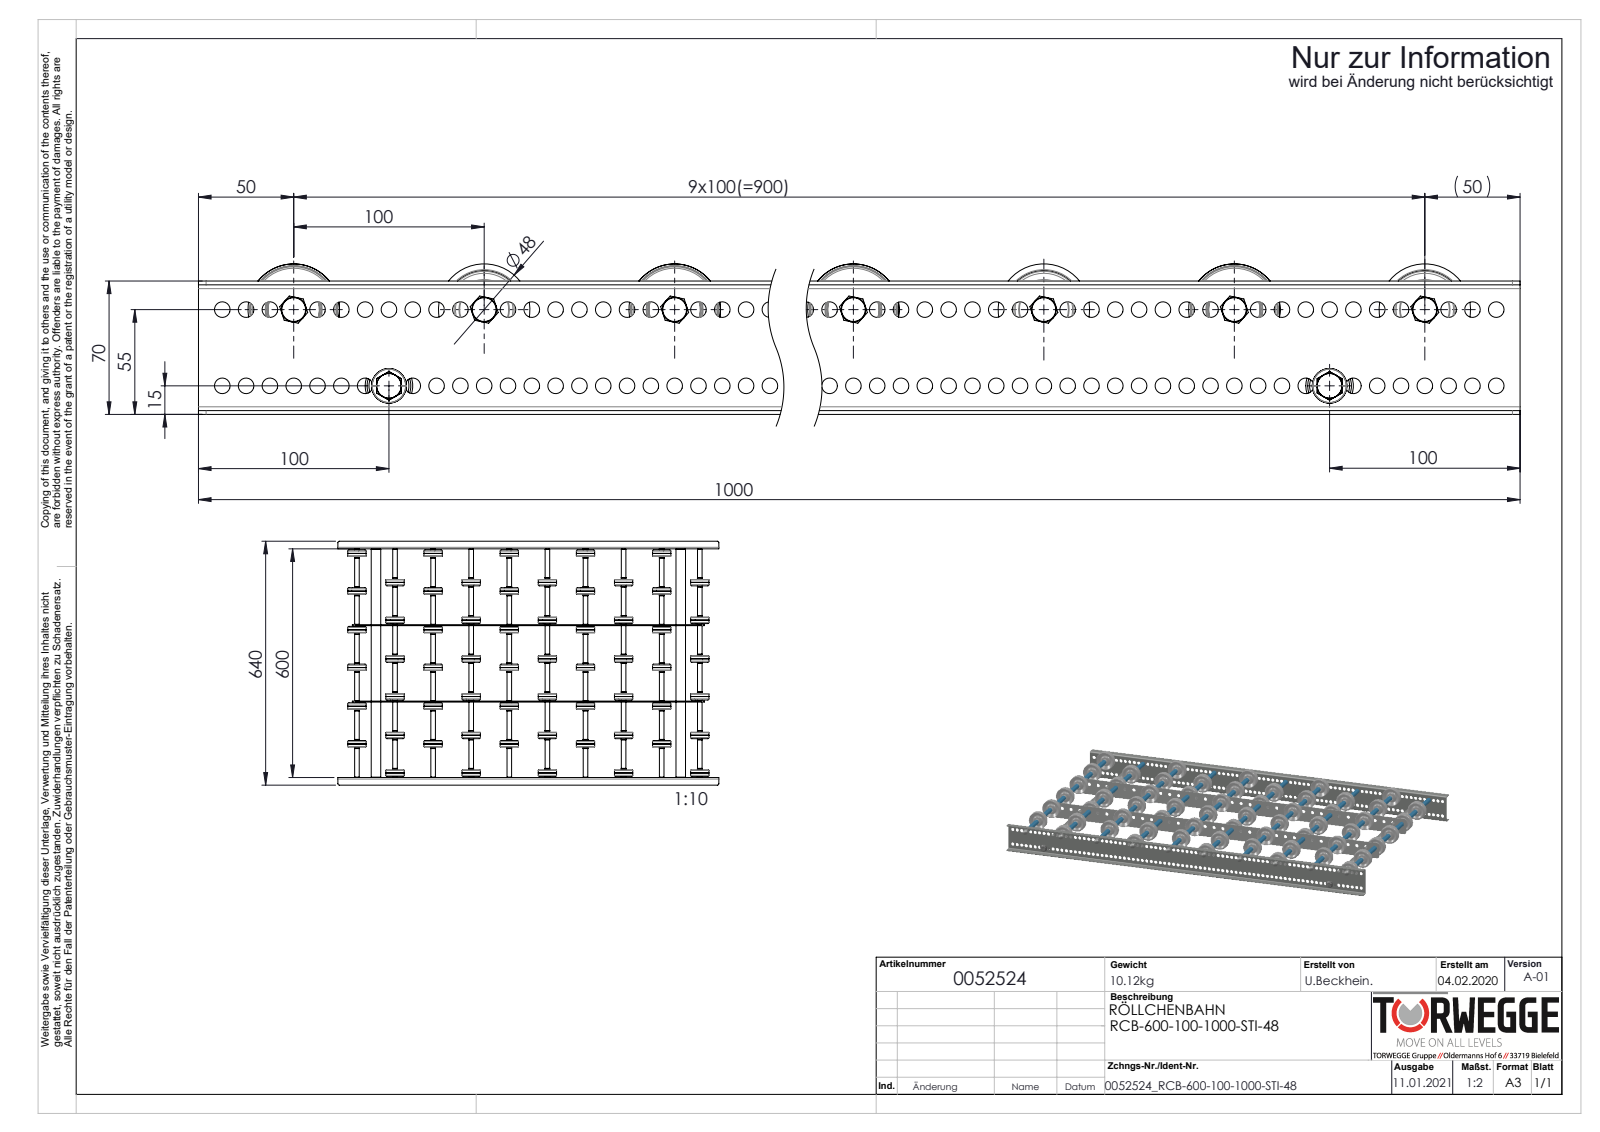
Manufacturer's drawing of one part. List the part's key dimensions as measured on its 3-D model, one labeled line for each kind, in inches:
Part name (STEP PRODUCT): Profil_LRB-20x70x20x2_KFG_S100200_U-PROFIL-20-70-20-2-LRB-L=1000; Traversen_KFG_L600; K0011528_2200-48-8; 0052524 (+6 more)
STEP written by: SolidWorks 2020 (AUTOMOTIVE_DESIGN)
Units: inches
Bodies: 224 solids, 6880 faces (1392 planar, 2744 cylindrical, 2744 other)
Overall size (bounding box): 39.37 × 25.197 × 3.11
Volume: 154.6 in³ · Surface area: 3 058 in²
Round holes (diameter × count): ⌀0.323 ×158, ⌀0.335 ×37, ⌀0.262 ×10, ⌀0.315 ×10, ⌀0.38 ×10, ⌀0.591 ×10, ⌀1.614 ×10, ⌀0.268 ×2, ⌀0.827 ×2
Round bosses / shafts (diameter × count): ⌀1.89 ×10, ⌀0.512 ×10, ⌀0.492 ×10, ⌀0.488 ×10, ⌀0.472 ×10, ⌀0.453 ×10, ⌀0.984 ×2, ⌀0.315 ×2
Partial cylindrical surfaces — rounded edges, fillets, slot ends (radius × count): R0.157 ×8, R0.079 ×4, R0.197 ×4
Main face-to-face distances: 7.894, 0.079, 23.701, 15.787, 2.992, 3.898, 0.098, 7.795, 4.37, 0.472
Hole centre spacings: 0.492, 0.984, 1.476, 1.969, 2.461, 2.953, 3.445, 3.937
